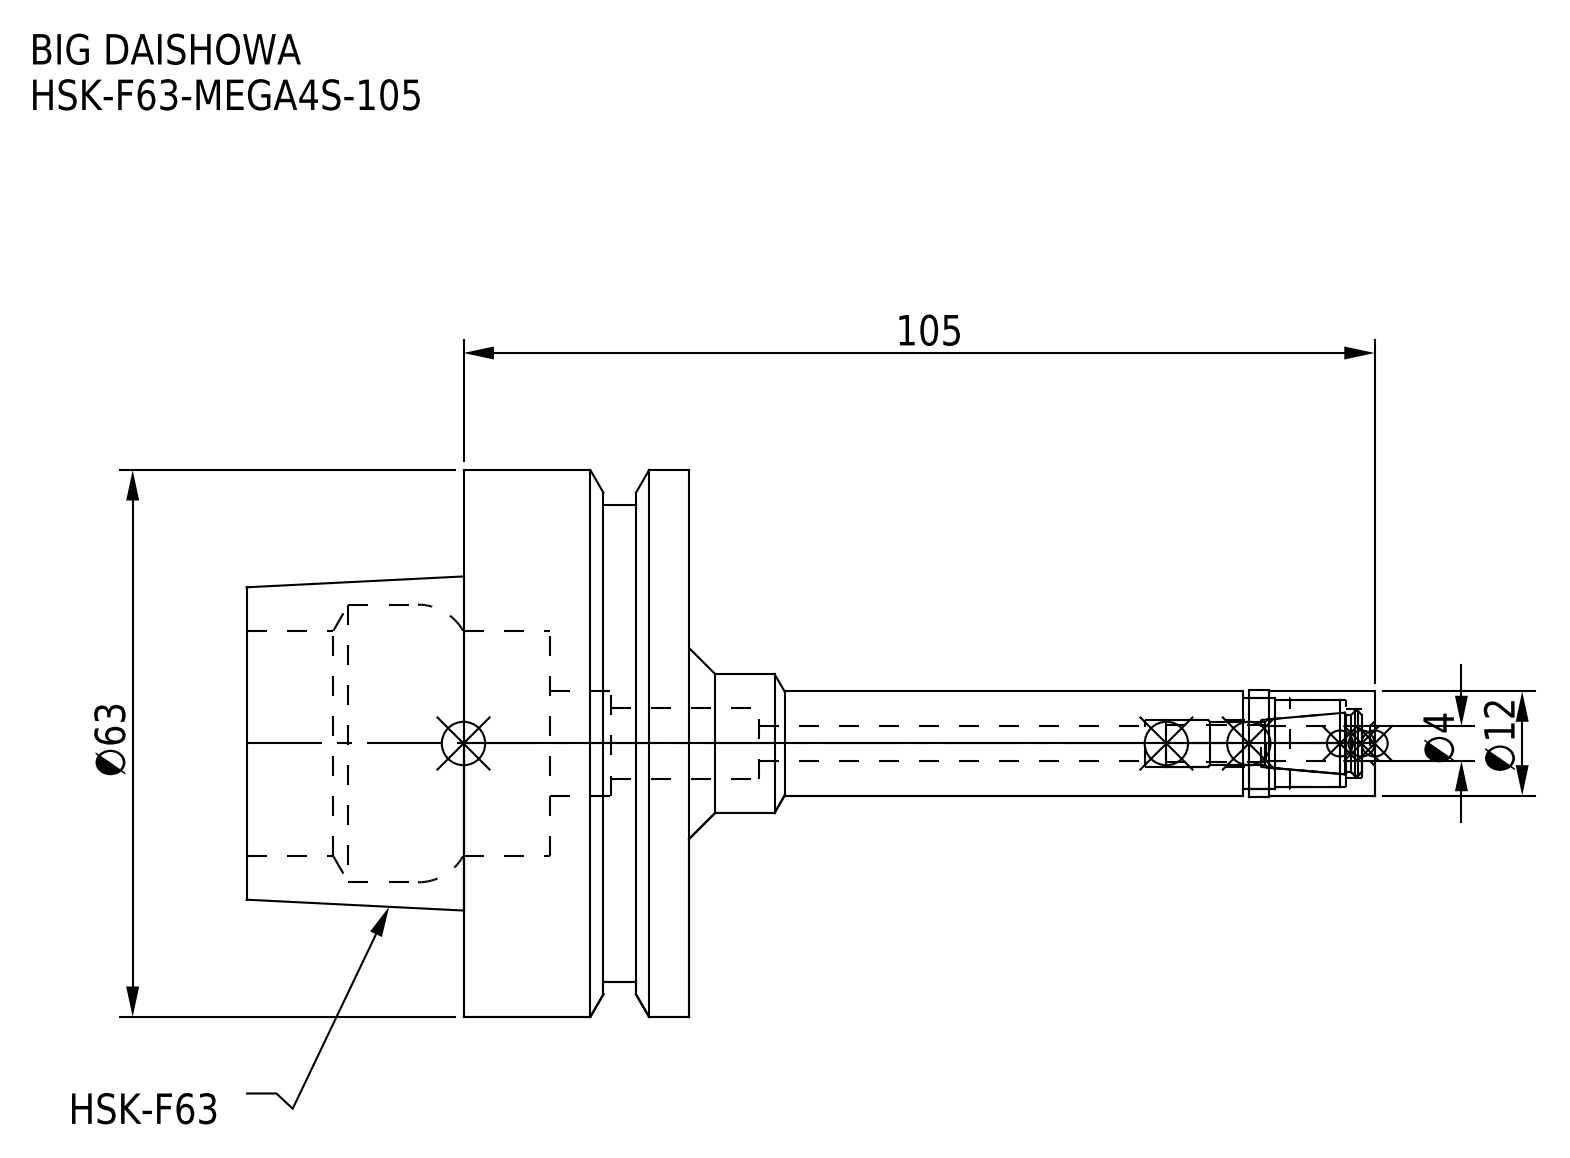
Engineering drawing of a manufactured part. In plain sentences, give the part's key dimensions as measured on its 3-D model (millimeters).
The part is named "HSK-F63-MEGA4S-105_1.stp; HSK-F63-MEGA4S-105-040-FreeParts; MGN4S_1.stp; HF63MS04105-040_ASM.stp (+3 more)". Its 3-D file was written by "SolidWorks 2019 (CONFIG_CONTROL_DESIGN)". It is 2 solids with 78 faces: 18 planar, 42 cylindrical and 18 other. Overall it measures 130 by 63 by 63 millimeters. Its volume is 89 849 cubic millimeters and its surface area 24 059 square millimeters. Round holes: 1 of diameter 4.1, 1 of diameter 5.4, 1 of diameter 8, 1 of diameter 8.25, 1 of diameter 10, 1 of diameter 10.5, 1 of diameter 26, 1 of diameter 32. Round bosses or shafts: 1 of diameter 63, 1 of diameter 55, 1 of diameter 16, 1 of diameter 12.3, 1 of diameter 12. The main face-to-face distances are 26, 25, 51, 16.05, 9.95, 34.95, 6.12, 9.93, 19.88, 44.88.
